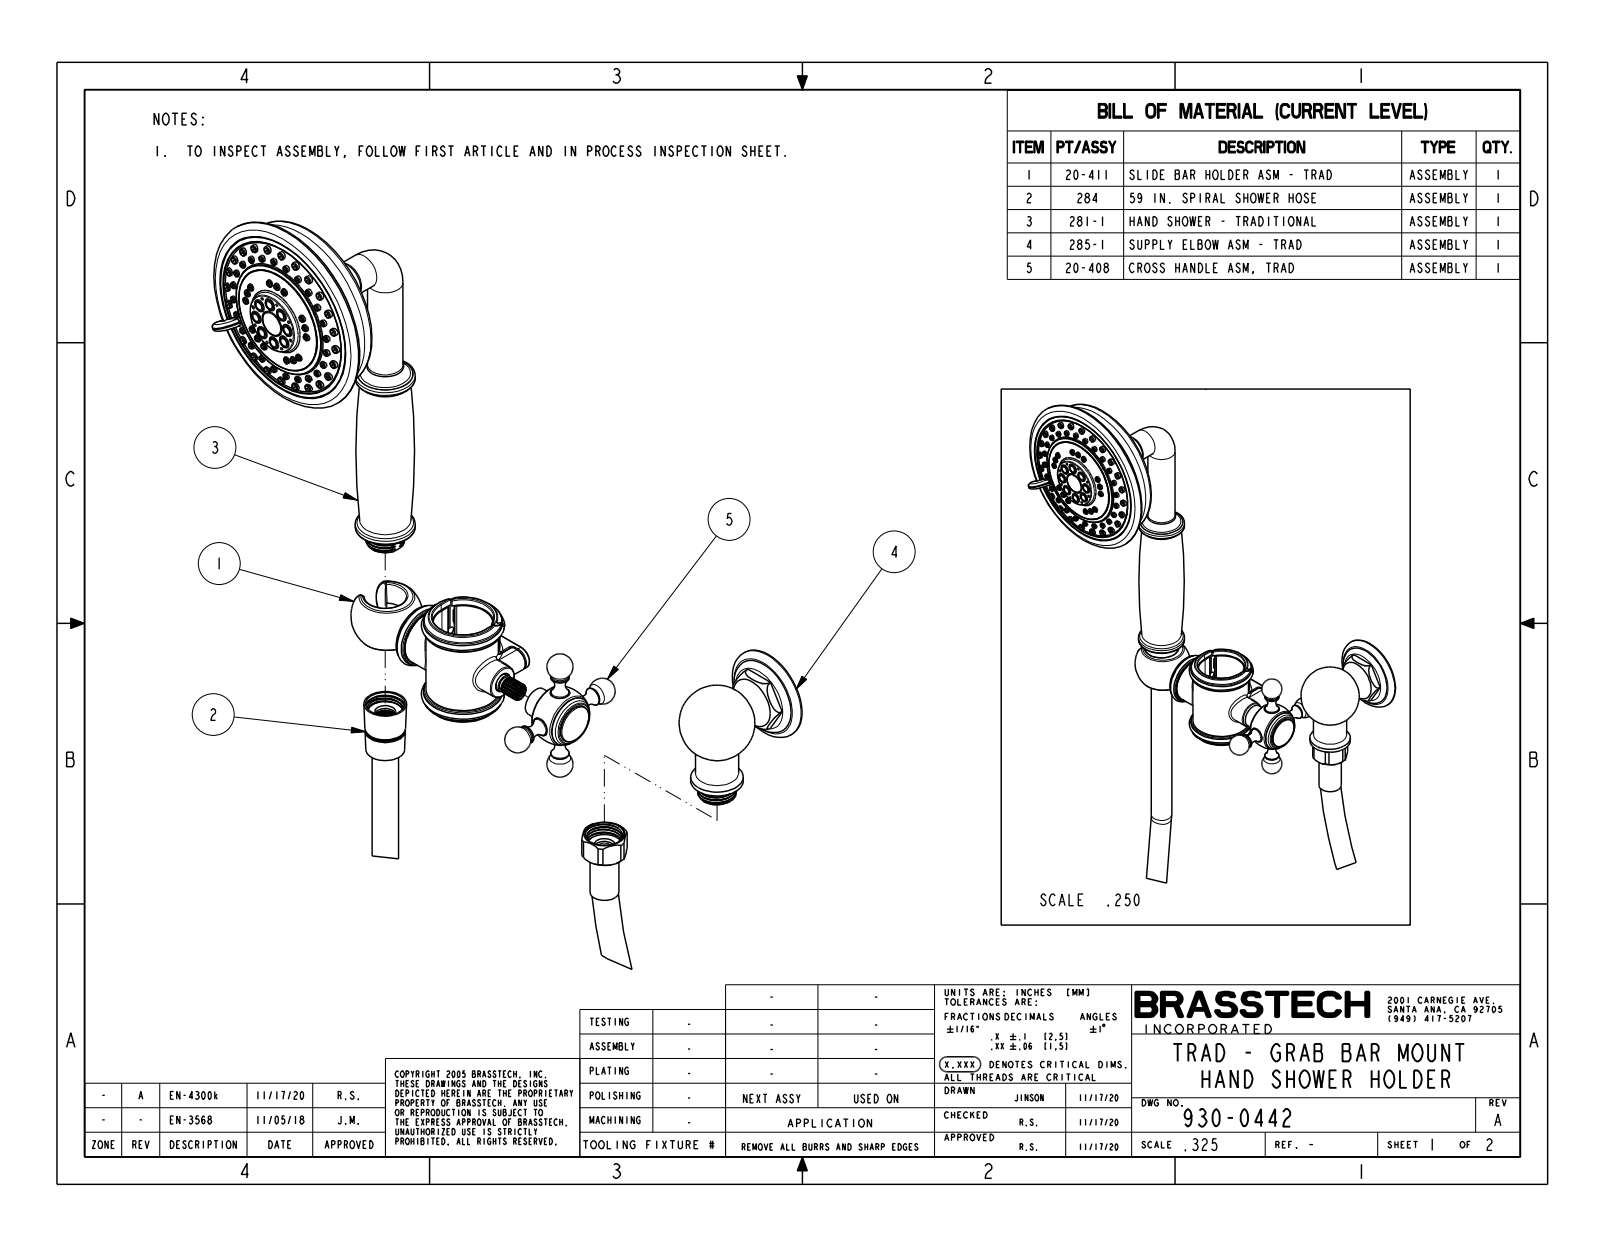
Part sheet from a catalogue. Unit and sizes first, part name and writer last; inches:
Units: inches
Overall size (bounding box): 29.637 × 15.302 × 5.533
Round holes (diameter × count): ⌀0.059 ×8, ⌀0.413 ×2, ⌀0.193 ×1, ⌀1.08 ×1, ⌀1.265 ×1, ⌀1.3 ×1, ⌀1.4 ×1
Round bosses / shafts (diameter × count): ⌀0.142 ×39, ⌀0.165 ×23, ⌀0.56 ×3, ⌀0.75 ×2, ⌀0.392 ×2, ⌀3.81 ×1, ⌀3.24 ×1, ⌀2.323 ×1
Partial cylindrical surfaces — rounded edges, fillets, slot ends (radius × count): R0.02 ×44, R0.06 ×8, R0.02 ×4, R0.03 ×4, R0.033 ×2, R0.25 ×2, R0.08 ×1, R0.122 ×1
Main face-to-face distances: 0.02, 1.175, 1.165, 1.28, 0.5, 0.017, 1.283, 1.263, 0.25, 1.3
Hole centre spacings: 0.443, 0.819, 1.069, 1.157, 0.443, 1.07, 0.818, 0.819
Volume: 43.48 in³ · Surface area: 244.2 in²
Bodies: 2 solids, 1521 faces (194 planar, 347 cylindrical, 980 other)
Part name (STEP PRODUCT): 930-0442
STEP written by: CREO PARAMETRIC BY PTC INC, 2018400 (CONFIG_CONTROL_DESIGN)
